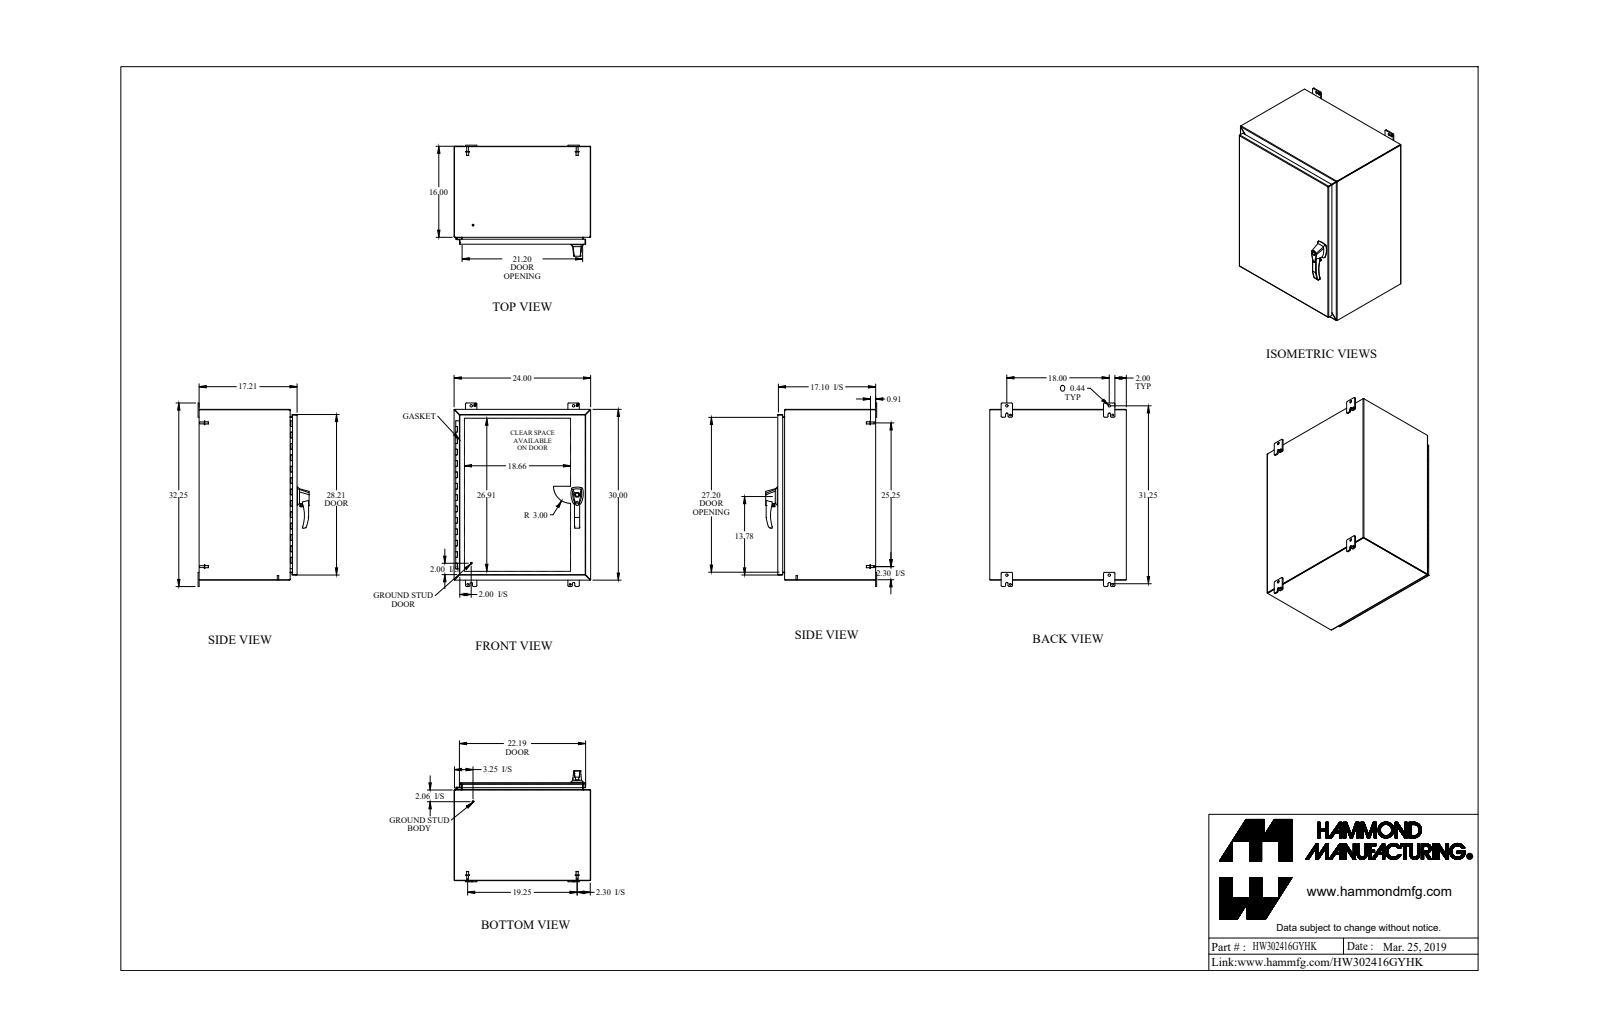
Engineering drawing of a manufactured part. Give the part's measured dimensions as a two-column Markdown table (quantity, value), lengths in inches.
| quantity | value |
| --- | --- |
| part name | HW302416GYHK |
| STEP written by | SolidWorks 2018 (AUTOMOTIVE_DESIGN) |
| units | inches |
| bodies | 43 solids, 1453 faces (699 planar, 589 cylindrical, 165 other) |
| overall size | 32.25 × 24 × 19.512 |
| volume | 283.2 in³ |
| surface area | 7 427 in² |
| round holes (diameter × count) | 0.176 × 6, 0.25 × 4, 0.313 × 4, 0.196 × 3, 0.265 × 3, 0.413 × 3, 0.256 × 2, 0.394 × 2, 0.437 × 2, 0.187 × 1, 0.233 × 1, 0.334 × 1 |
| round bosses / shafts (diameter × count) | 0.375 × 9, 0.25 × 6, 0.156 × 6, 0.65 × 4, 0.33 × 4, 1 × 3, 0.63 × 2, 0.51 × 2 |
| partial cylindrical surfaces (radius × count) | 0.25 × 31, 0.188 × 24, 0.036 × 18, 0.108 × 18, 0.06 × 12, 0.125 × 9, 0.04 × 8, 0.218 × 8 |
| main face-to-face distances | 0.072, 23.928, 29.928, 0.072, 17.138, 17.066, 17.21, 17.138, 23.856, 24 |
| hole center spacings | 11.118, 11.119, 22.237, 1.111, 9.698, 11.119, 18, 31.381 |
